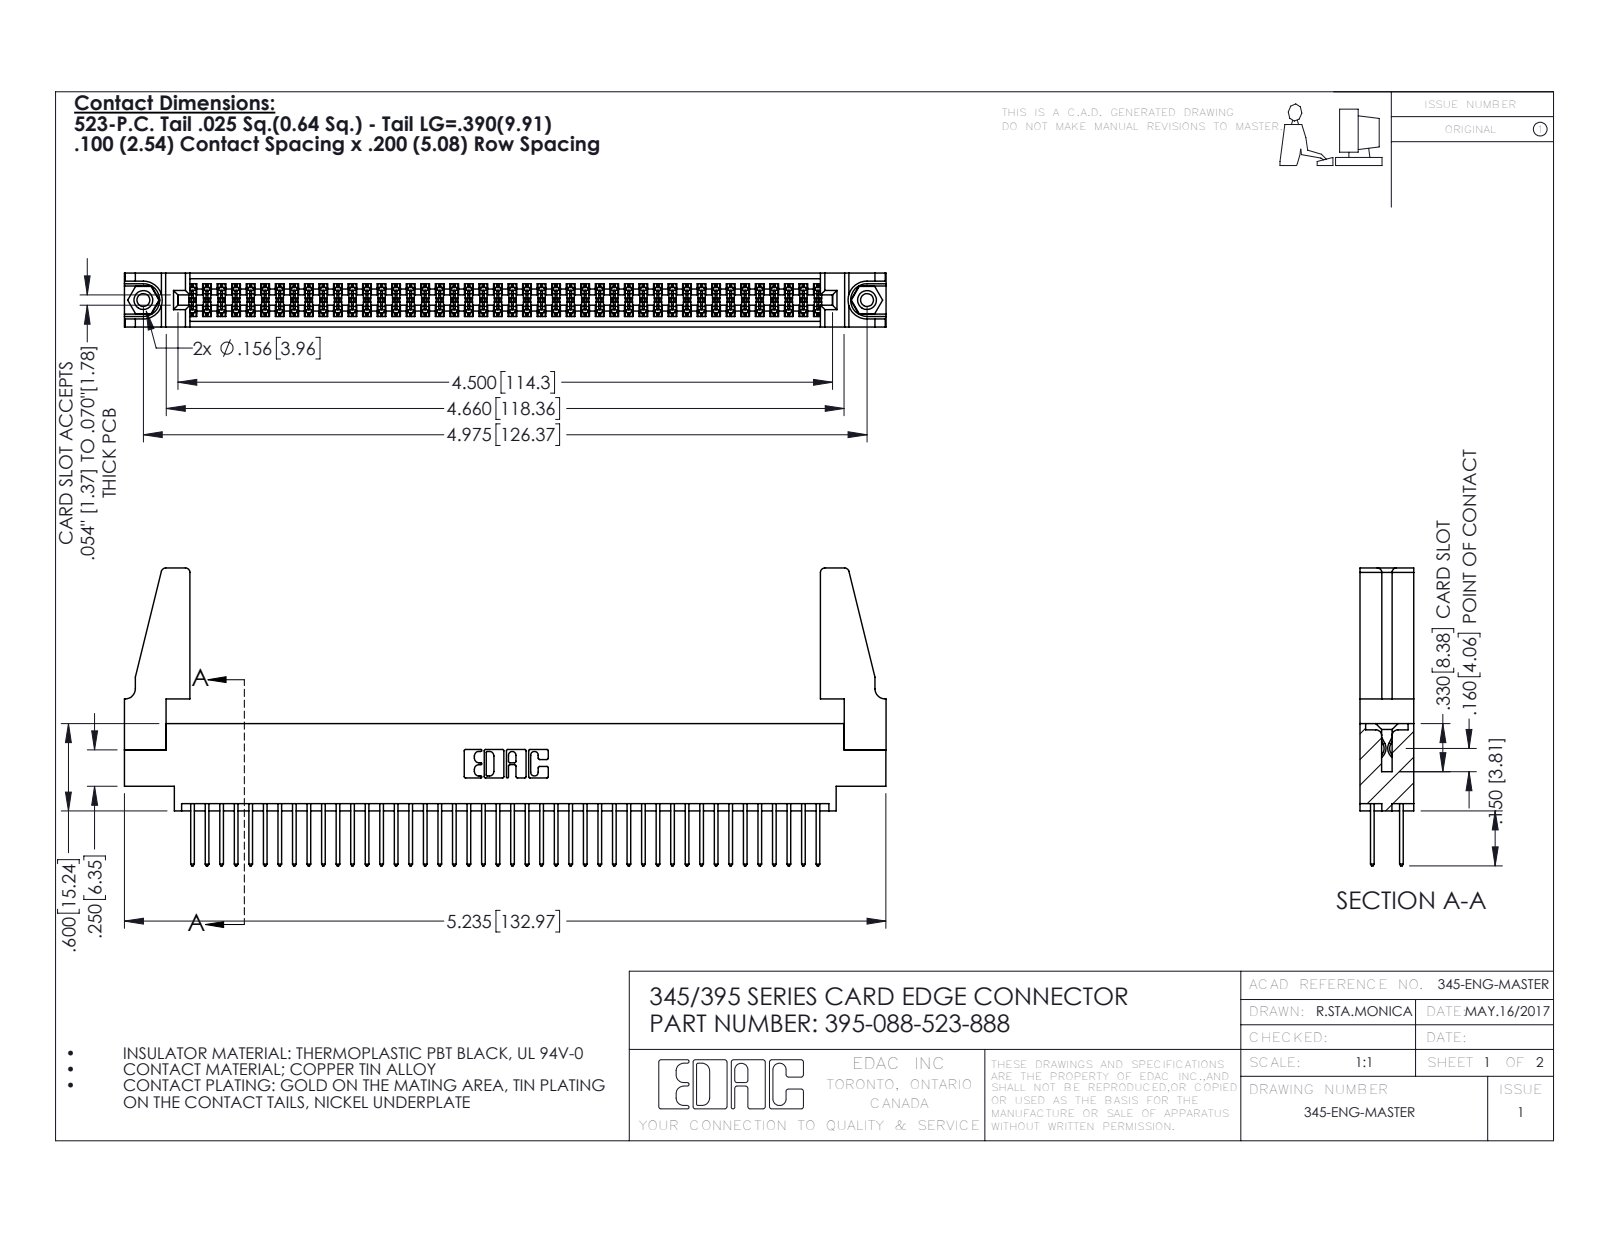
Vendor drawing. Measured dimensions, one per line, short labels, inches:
name: 345-292-001_345-293-123; 345-220-078_345-220-088; 395-088-523-888; 345-250-001_345-250-001-102 (+1 more)
written by: SolidWorks 2016 (CONFIG_CONTROL_DESIGN)
unit: in
bodies: 93 solids, 4654 faces (3060 planar, 1578 cylindrical, 16 other)
size: 5.236 × 2.047 × 0.37
volume: 0.992 in³; area: 36.17 in²
holes: 2× ⌀0.089, 2× ⌀0.125, 2× ⌀0.156, 1× ⌀0.064
bosses: 2× ⌀0.155
rounds: 132× R0.006, 88× R0.01, 22× R0.01, 8× R0.03, 6× R0.007, 6× R0.031, 3× R0.026, 2× R0.014
face distances: 0.072, 0.298, 0.37, 0.2, 0.098, 0.272, 0.025, 0.225, 0.175, 0.149
hole spacings: 0.27, 4.739, 4.975
